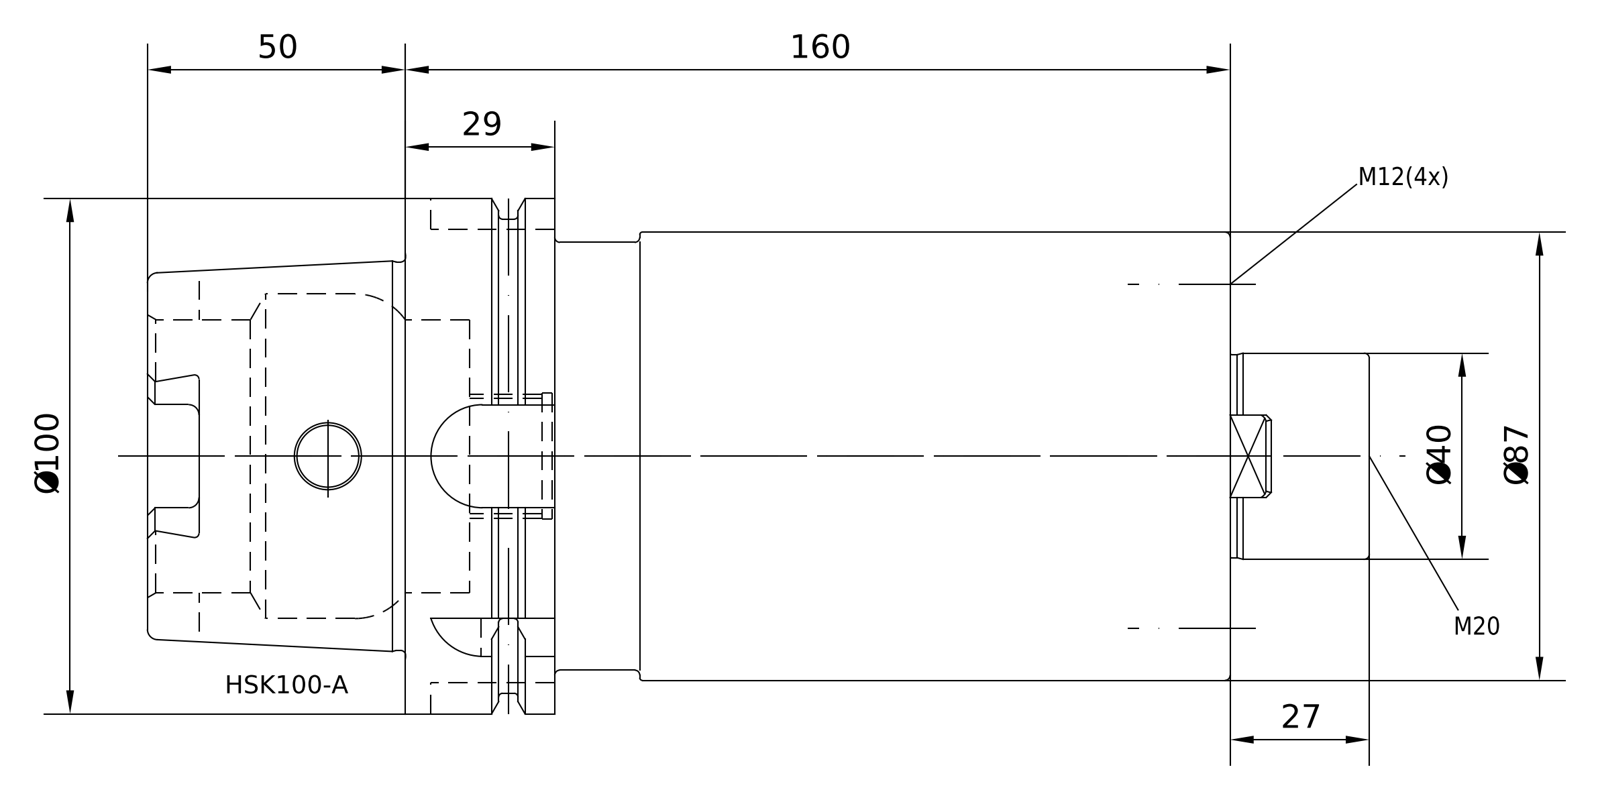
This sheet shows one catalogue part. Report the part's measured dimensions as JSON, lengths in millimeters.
{"part_name": "A100-052-40", "step_written_by": "PRO/ENGINEER BY PARAMETRIC TECHNOLOGY CORPORATION, 2010430 (CONFIG_CONTROL_DESIGN)", "units": "millimeters", "bodies": {"solids": 1, "faces": 226, "planar": 66, "cylindrical": 73, "other": 87}, "overall_size": [237, 100, 100], "volume_mm3": 1042000, "surface_area_mm2": 101989, "round_holes": [[12, 5], [10.2, 4], [10, 1], [17.5, 1], [20, 1], [22.5, 1], [24, 1], [24.32, 1], [24.5, 1], [53, 1], [63, 1]], "round_bosses_or_shafts": [[100, 1], [92, 1], [87, 1], [83, 1], [75.36, 1], [40, 1]], "partial_cylinders_radius": [[2, 6], [5, 4], [8, 1], [10, 1], [11, 1]], "face_to_face_distances": [160, 29, 131, 12.5, 16.5, 147.5, 79, 16, 187, 174.5], "hole_center_spacings": [33.35, 47.16, 66.69]}
